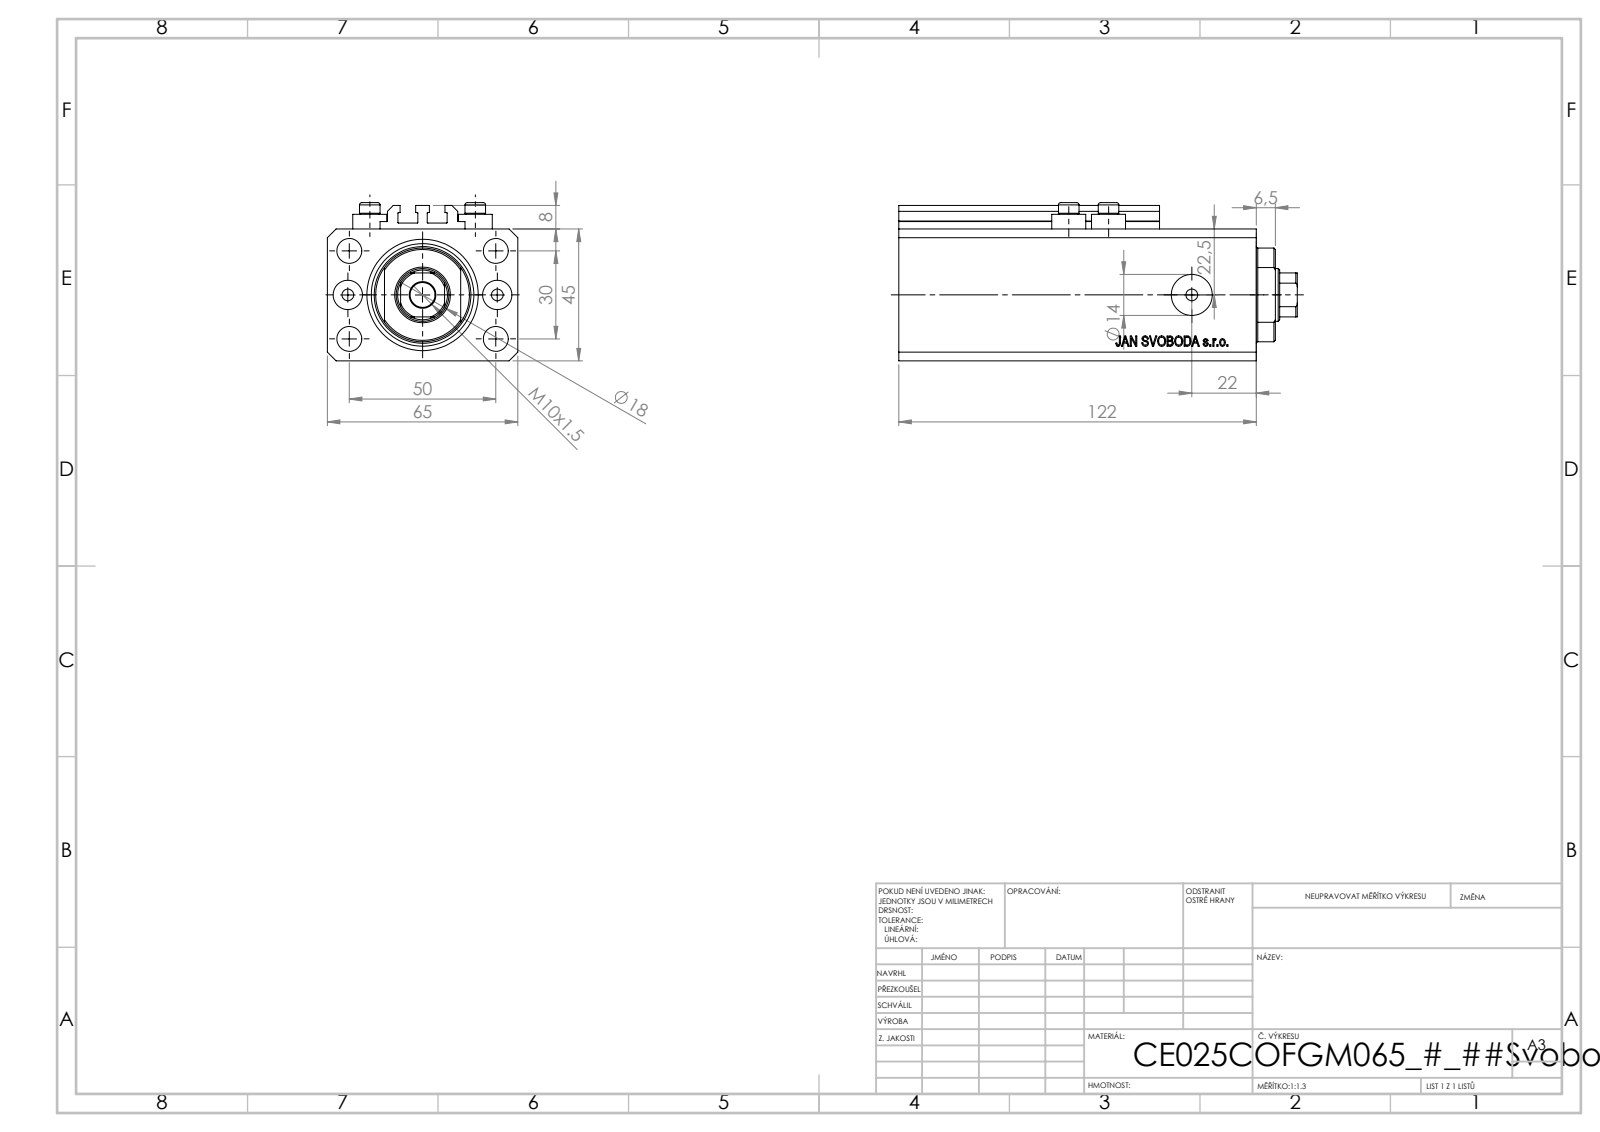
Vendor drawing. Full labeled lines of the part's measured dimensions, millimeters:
Part name (STEP PRODUCT): ALLEN BOLT V250CE; V250CE_VC_C; V250CE_C_Body; V250CE_C_VCP
STEP written by: SolidWorks 2019 (CONFIG_CONTROL_DESIGN)
Units: millimetres
Bodies: 8 solids, 1034 faces (504 planar, 86 cylindrical, 444 other)
Overall size (bounding box): 136 × 65 × 54
Volume: 327 580 mm³ · Surface area: 82 271 mm²
Round holes (diameter × count): ⌀4 ×8, ⌀8.5 ×5, ⌀10 ×2, ⌀14 ×2, ⌀18 ×1, ⌀25 ×1, ⌀38 ×1
Round bosses / shafts (diameter × count): ⌀11.6 ×4, ⌀7 ×4
Partial cylindrical surfaces — rounded edges, fillets, slot ends (radius × count): R0.2 ×10, R8.5 ×1, R16 ×1
Main face-to-face distances: 45, 65, 14, 47, 108, 122, 2.5, 10, 2, 20.5
Hole centre spacings: 15.01, 29.15, 52.68, 13.6, 25.5, 30, 36, 38.48
